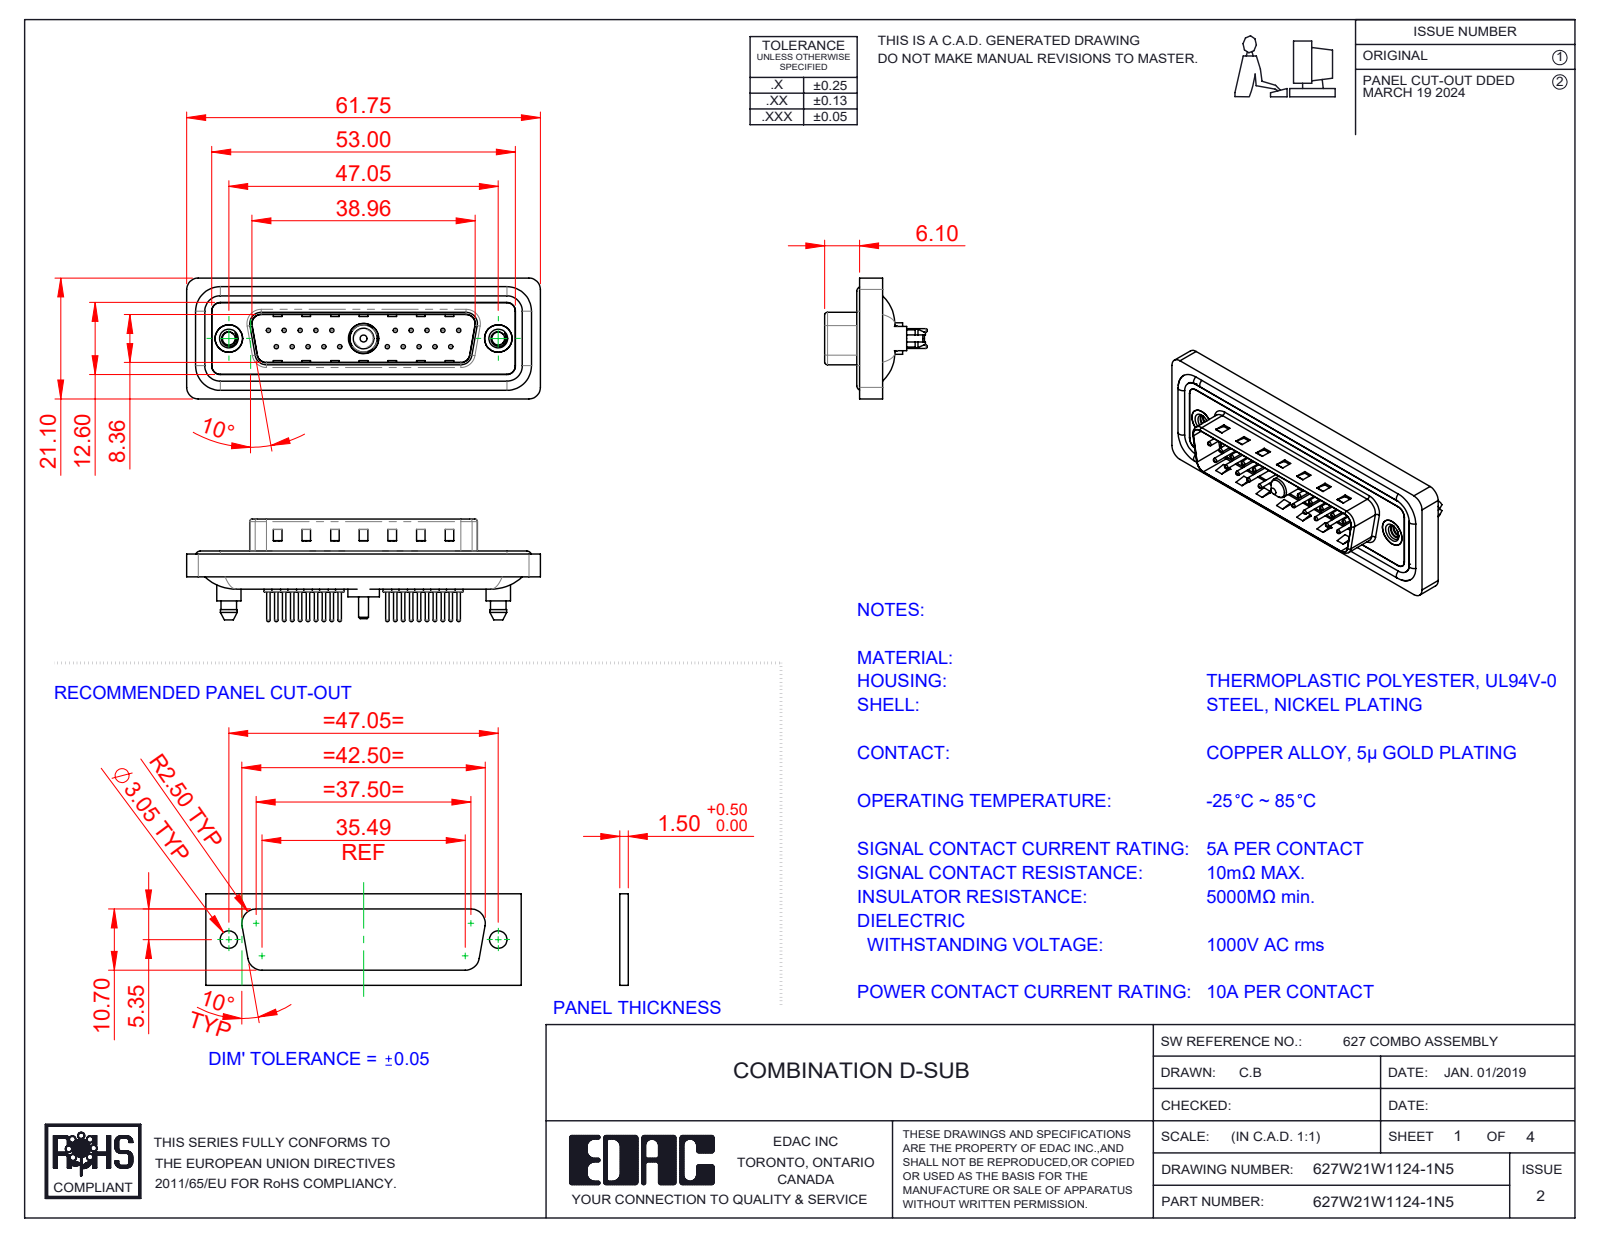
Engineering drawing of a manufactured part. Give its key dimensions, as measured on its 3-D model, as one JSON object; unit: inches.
{"part_name": "627Combo Shell Front_25 Contacts; 627W21W1124-1N5; 627Combo Contact Row 1_24; 627Combo Threaded Boardlock_5 (+5 more)", "step_written_by": "SolidWorks 2023 (CONFIG_CONTROL_DESIGN)", "units": "inches", "bodies": {"solids": 29, "faces": 1312, "planar": 375, "cylindrical": 519, "other": 418}, "overall_size": [2.431, 0.831, 0.705], "volume_in3": 0.447, "surface_area_in2": 19.02, "round_holes": [[0.03, 20], [0.063, 20], [0.079, 20], [0.089, 2], [0.157, 2], [0.189, 2], [0.197, 2], [0.191, 1], [0.209, 1]], "round_bosses_or_shafts": [[0.059, 20], [0.024, 20], [0.063, 4], [0.213, 2], [0.193, 2], [0.167, 2], [0.217, 1], [0.205, 1]], "partial_cylinders_radius": [[0.059, 24], [0.079, 18], [0.063, 10], [0.02, 8], [0.01, 4], [0.024, 4], [0.026, 4], [0.035, 4]], "face_to_face_distances": [0.016, 0.059, 0.043, 0.063, 0.02, 0.122, 0.114, 0.161, 0.032, 0.377], "hole_center_spacings": [0.124, 0.109, 0.218, 0.327, 0.198, 0.763, 0.826, 0.872]}
